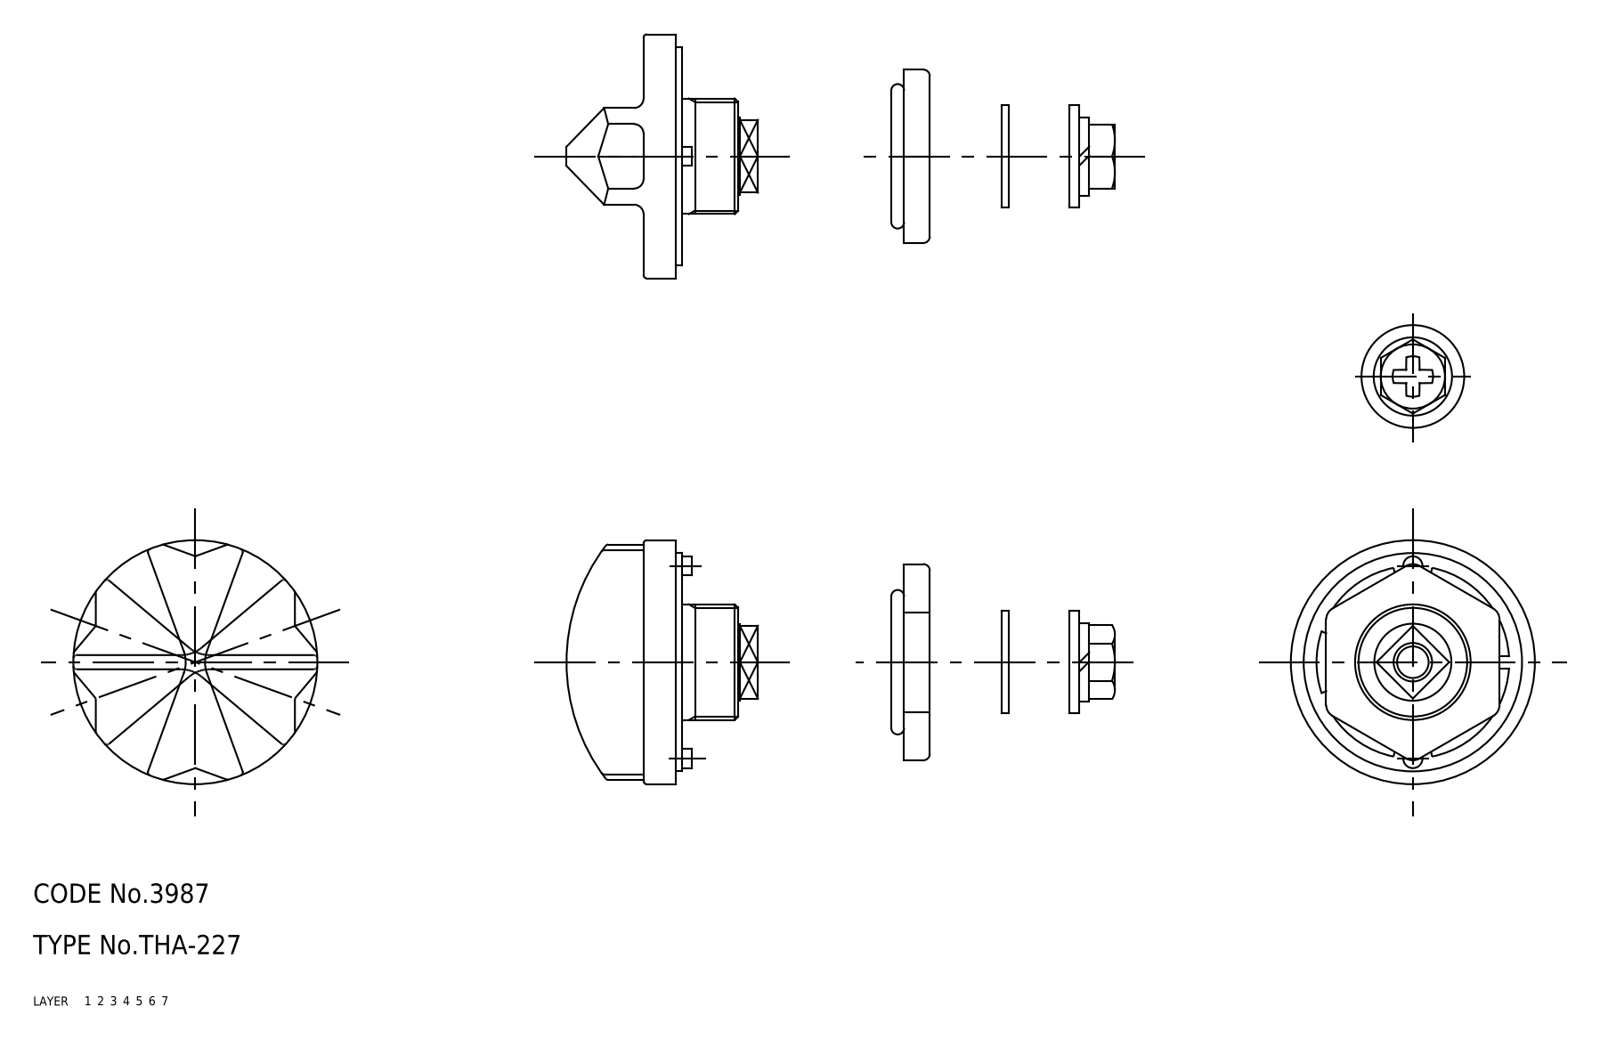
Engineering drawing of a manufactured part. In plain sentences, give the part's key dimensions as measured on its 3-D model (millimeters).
The part is named "THA_227". Its 3-D file was written by "SolidWorks 2003240 (AUTOMOTIVE_DESIGN)". It is 7 solids with 232 faces: 86 planar, 89 cylindrical and 57 other. Overall it measures 38 by 38 by 36.9 millimeters. Its volume is 13 618 cubic millimeters and its surface area 10 903 square millimeters. Round holes: 1 of diameter 6, 1 of diameter 12, 1 of diameter 18, 1 of diameter 20.3, 1 of diameter 30, 1 of diameter 34. Round bosses or shafts: 2 of diameter 3, 1 of diameter 38, 1 of diameter 20.7, 1 of diameter 20, 1 of diameter 16, 1 of diameter 12.2. Partial cylindrical surfaces (rounded edges, fillets, slot ends): 8 of radius 0.5, 8 of radius 1.5, 6 of radius 1, 6 of radius 2, 2 of radius 3, 2 of radius 5, 1 of radius 3.15, 1 of radius 30. The main face-to-face distances are 3, 2.5, 5, 2, 0.5, 6, 8, 4, 12, 9.
